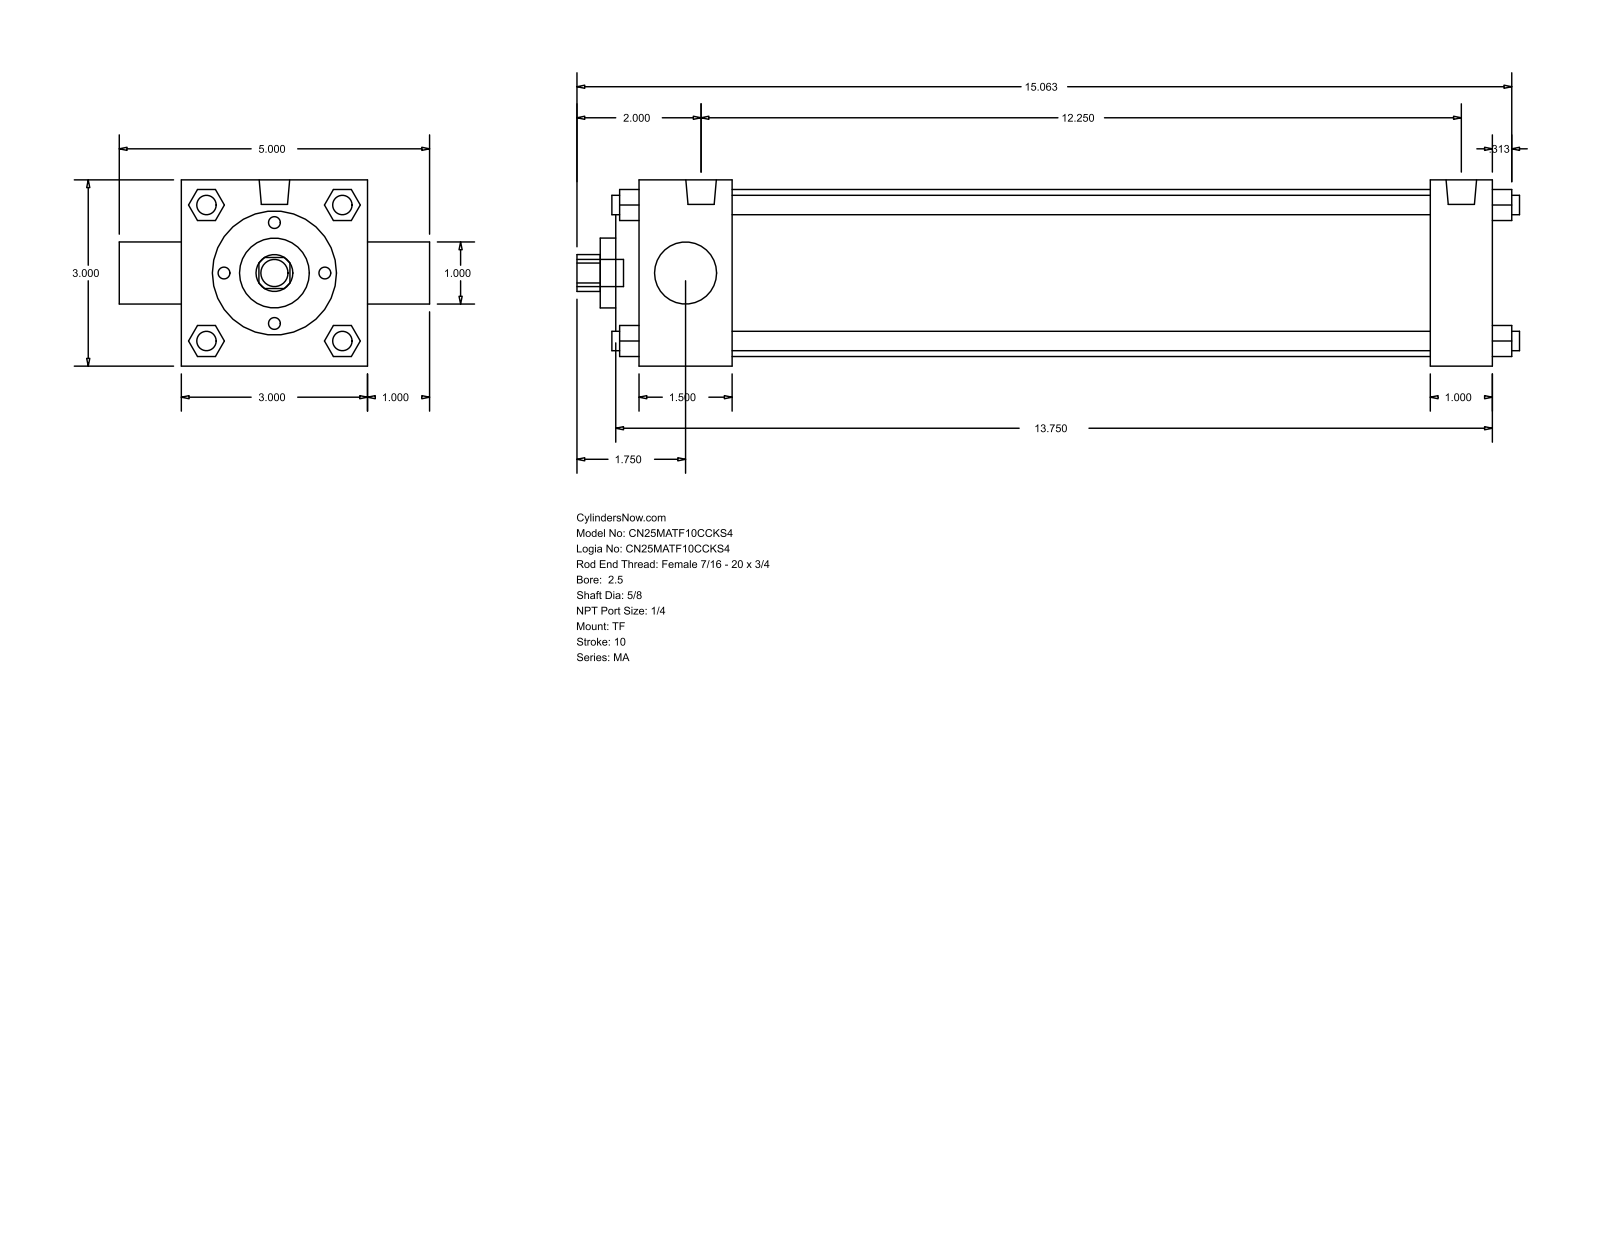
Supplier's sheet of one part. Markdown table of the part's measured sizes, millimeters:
| quantity | value |
| --- | --- |
| part name | MA_TF__0250_0.625 |
| STEP written by | GSSL Pune (CONFIG_CONTROL_DESIGN) |
| units | millimeters |
| bodies | 0 solids, 122 faces (93 planar, 29 cylindrical, 0 other) |
| overall size | 385.76 × 127 × 76.2 |
| round holes (diameter × count) | 15.88 × 1, 25.4 × 1, 28.57 × 1, 50.8 × 1, 68.33 × 1 |
| round bosses / shafts (diameter × count) | 7.94 × 7, 12.49 × 2, 11.11 × 1 |
| partial cylindrical surfaces (radius × count) | 7.54 × 1 |
| main face-to-face distances | 76.2, 349.25, 25.4, 38.1, 323.85, 285.75, 311.15, 12.7, 9.52, 47.62 |
